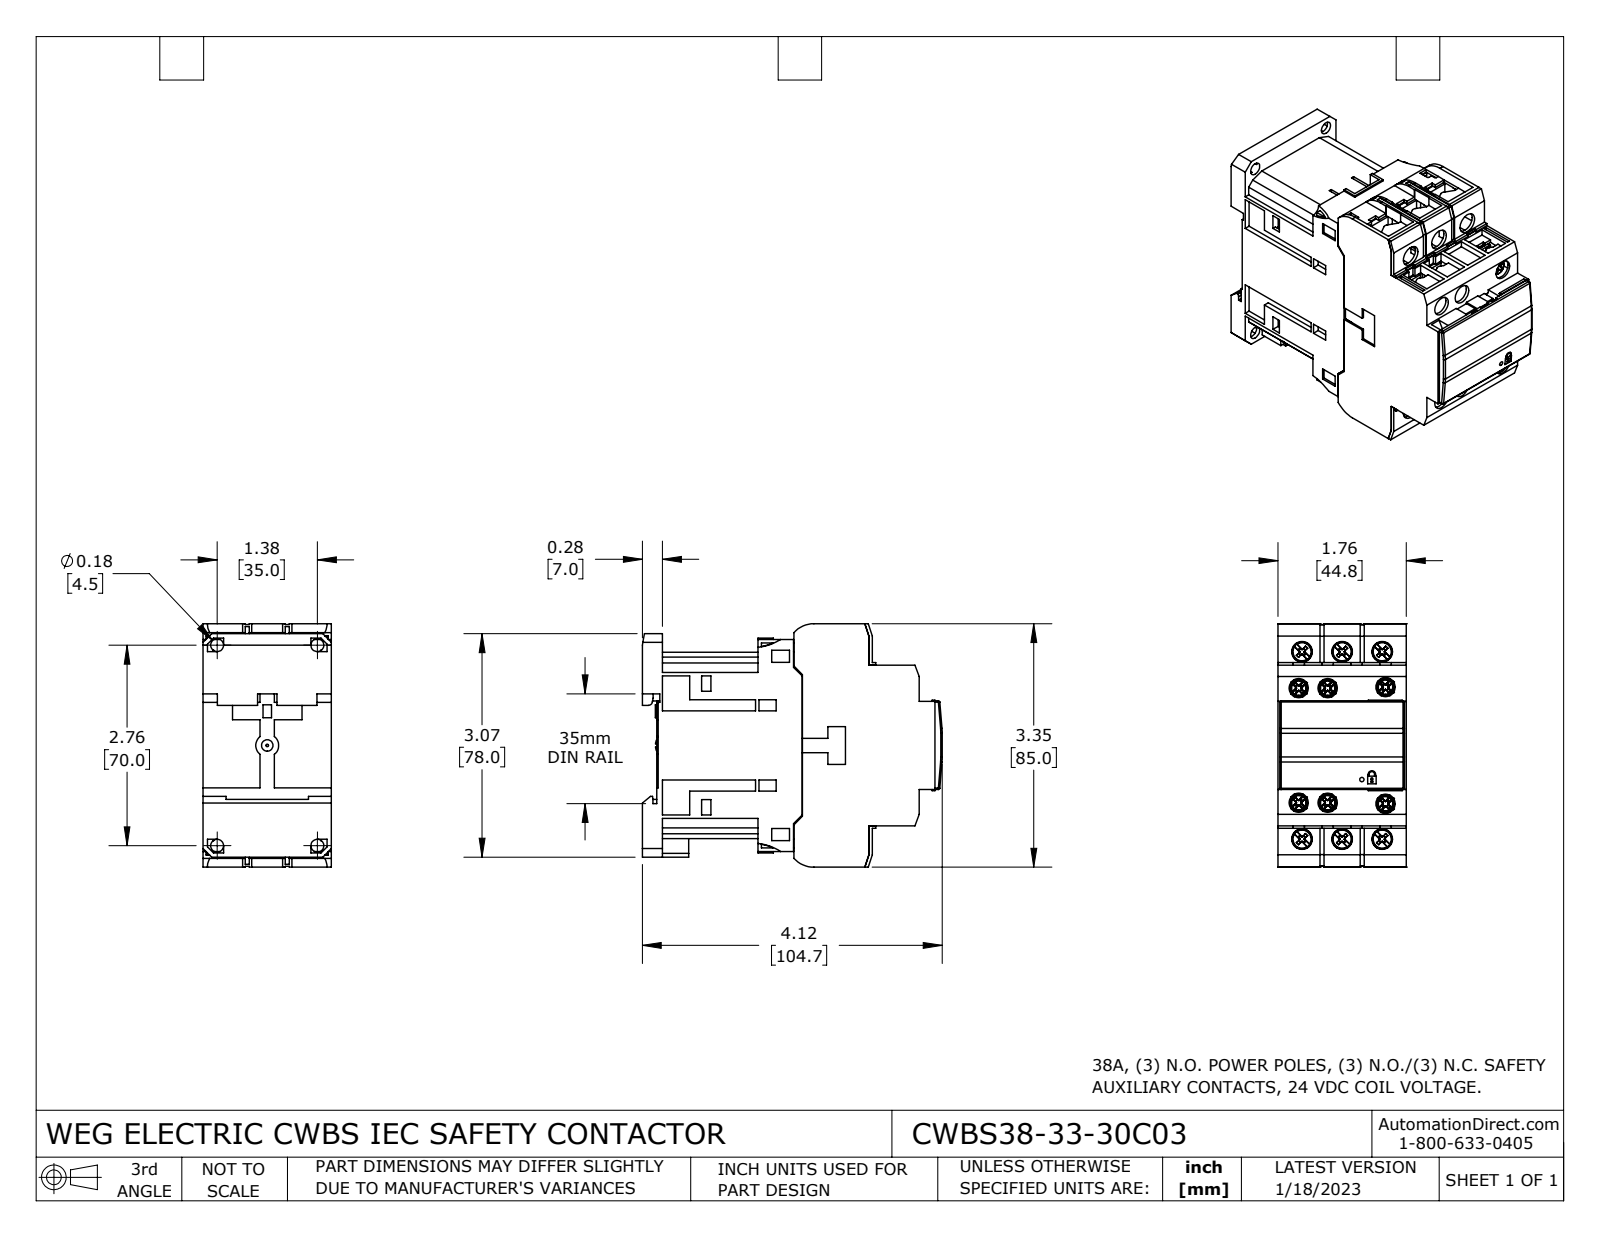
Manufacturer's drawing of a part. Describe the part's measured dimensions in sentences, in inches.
The part is named "CWBS38-33-30C03". Its 3-D file was written by "SolidWorks 2021 (CONFIG_CONTROL_DESIGN)". It is 42 solids with 3062 faces: 1894 planar, 647 cylindrical and 521 other. Overall it measures 4.122 by 3.346 by 1.764 inches. Its volume is 16.15 cubic inches and its surface area 115.3 square inches. Round holes: 6 of diameter 0.124, 6 of diameter 0.142, 6 of diameter 0.264, 6 of diameter 0.283, 4 of diameter 0.177, 2 of diameter 0.236, 1 of diameter 0.059. Round bosses or shafts: 6 of diameter 0.201, 6 of diameter 0.169, 6 of diameter 0.157, 6 of diameter 0.138, 6 of diameter 0.107. Partial cylindrical surfaces (rounded edges, fillets, slot ends): 72 of radius 0.008, 54 of radius 0.012, 48 of radius 0.004, 37 of radius 0.02, 24 of radius 0.028, 12 of radius 0.071, 12 of radius 0.081, 12 of radius 0.964. The main face-to-face distances are 1.764, 0.047, 1.823, 1.827, 0.024, 0.272, 0.646, 0.217, 3.807, 0.094. The hole center spacings are 0.165, 0.551, 0.664, 0.695, 0.829, 1.243, 2.272, 2.396.
